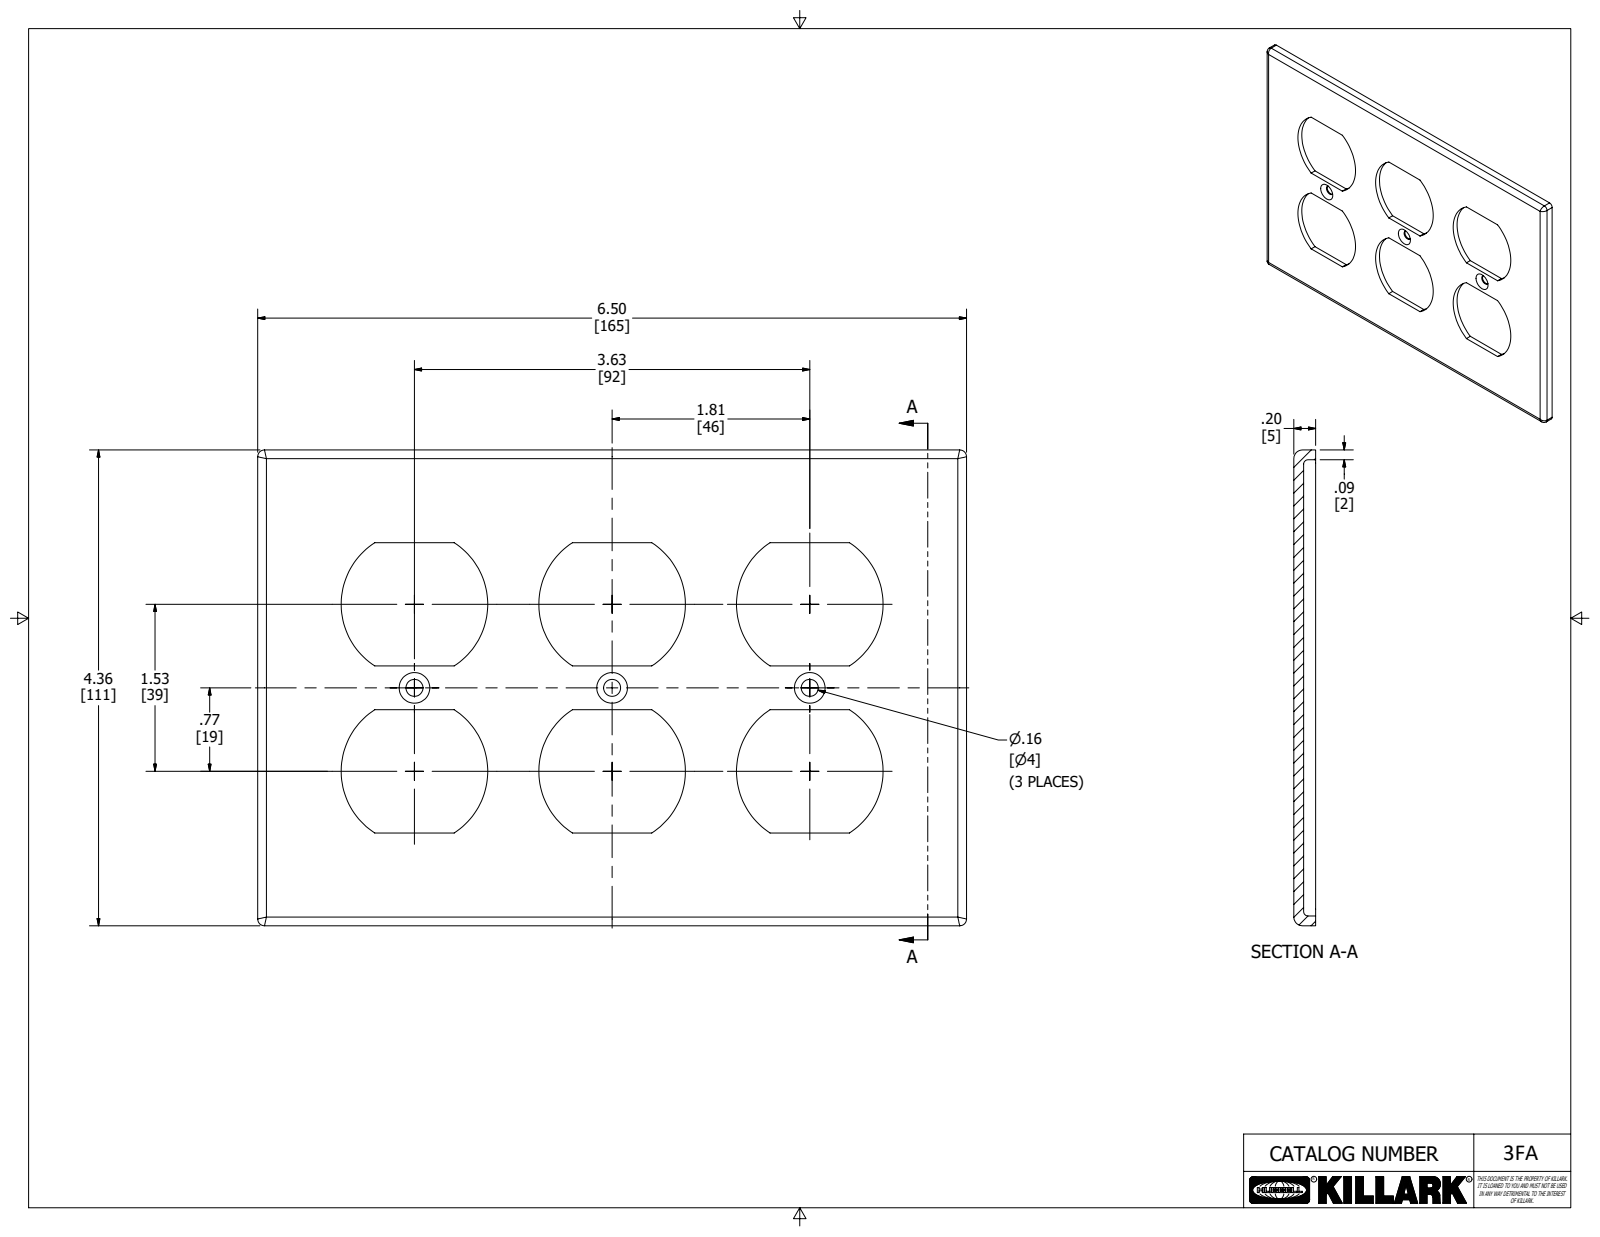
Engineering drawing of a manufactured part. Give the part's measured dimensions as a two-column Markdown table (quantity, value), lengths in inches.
| quantity | value |
| --- | --- |
| part name | 07806-4 |
| STEP written by | Autodesk Inventor 2020 (AUTOMOTIVE_DESIGN) |
| units | inches |
| bodies | 1 solid, 65 faces (23 planar, 31 cylindrical, 11 other) |
| overall size | 6.5 × 4.362 × 0.2 |
| volume | 2.022 in³ |
| surface area | 48.68 in² |
| round holes (diameter × count) | 0.156 × 3 |
| partial cylindrical surfaces (radius × count) | 0.062 × 6, 0.672 × 6, 0.04 × 4, 0.08 × 4, 0.031 × 2 |
| main face-to-face distances | 0.09, 0.11, 0.2, 4.272, 4.362, 6.41, 6.5, 4.182, 1.13, 1.531 |
| hole center spacings | 1.813, 3.625 |
